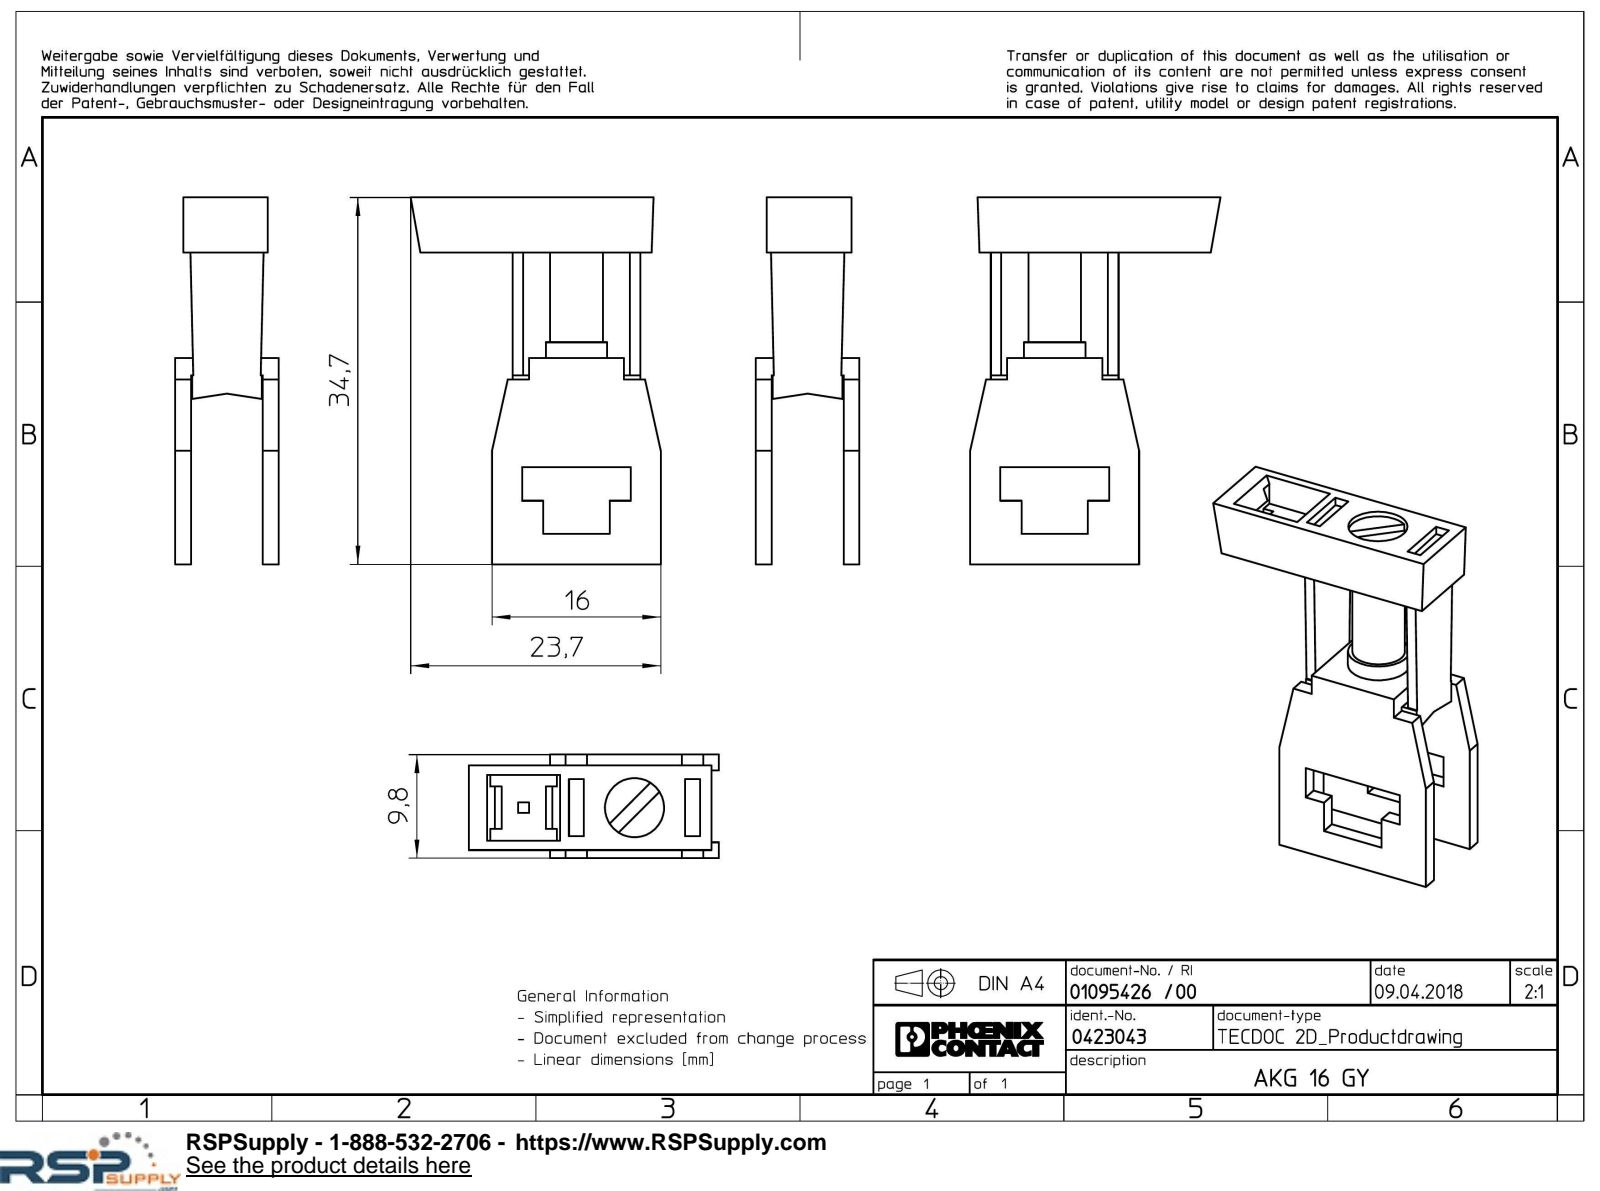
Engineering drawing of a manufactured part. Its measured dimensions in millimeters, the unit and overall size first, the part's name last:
Units: millimetres
Overall size (bounding box): 34.7 × 23.7 × 9.8
Round holes (diameter × count): ⌀5.6 ×1
Round bosses / shafts (diameter × count): ⌀5.8 ×1, ⌀5 ×1
Main face-to-face distances: 8.3, 1.5, 9.8, 6.8, 1, 11.1, 0.46, 0.74, 1.04, 9.04
Volume: 2 087 mm³ · Surface area: 2 775 mm²
Bodies: 1 solid, 104 faces (98 planar, 6 cylindrical, 0 other)
Part name (STEP PRODUCT): AKG_16_GY-Select
STEP written by: Creo Elements/Direct Modeling 20.1A 29-Sep-2018 (C) Parametric Technology GmbH (AUTOMOTIVE_DESIGN)
